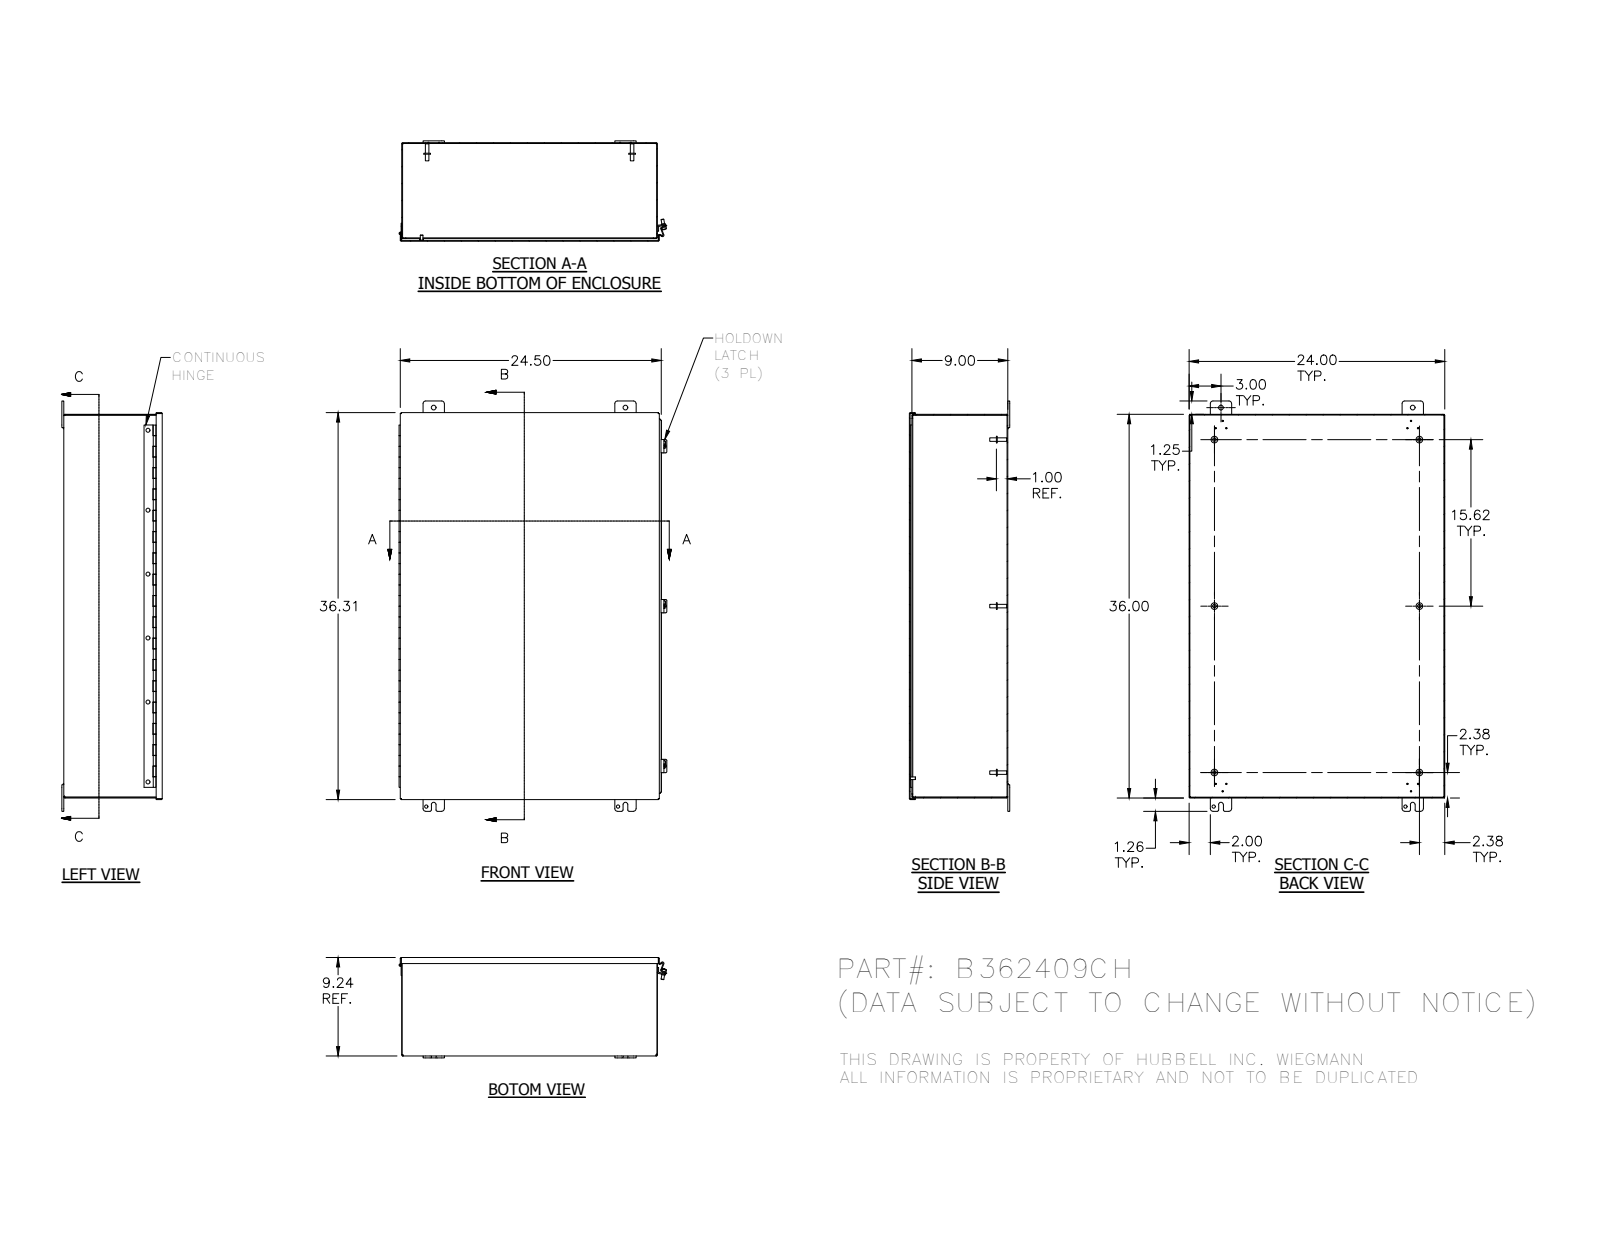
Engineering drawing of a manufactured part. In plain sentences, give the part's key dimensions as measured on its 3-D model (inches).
The part is named "B362409CH; B362409CHBKP; B3624CHLID; H6010103 (+8 more)". Its 3-D file was written by "Autodesk Inventor 2012 (AUTOMOTIVE_DESIGN)". It is 25 solids with 838 faces: 519 planar, 241 cylindrical and 78 other. Overall it measures 38.505 by 25.136 by 9.423 inches. Its volume is 224.7 cubic inches and its surface area 6 077 square inches. Round holes: 6 of diameter 0.11, 6 of diameter 0.375, 4 of diameter 0.313, 4 of diameter 0.438, 3 of diameter 0.196, 1 of diameter 0.125, 1 of diameter 0.125. Round bosses or shafts: 6 of diameter 0.625, 6 of diameter 0.33, 5 of diameter 0.25, 3 of diameter 0.41, 3 of diameter 0.344, 1 of diameter 0.337, 1 of diameter 0.12. Partial cylindrical surfaces (rounded edges, fillets, slot ends): 20 of radius 0.125, 16 of radius 0.25, 12 of radius 0.063, 8 of radius 0.031, 8 of radius 0.07, 8 of radius 0.105, 6 of radius 0.133, 5 of radius 0.016. The main face-to-face distances are 0.074, 9.169, 9.243, 9.095, 23.926, 35.926, 24, 23.852, 36, 35.852. The hole center spacings are 18, 15, 0.75, 6, 1.134, 1.593, 1.593, 1.881.
